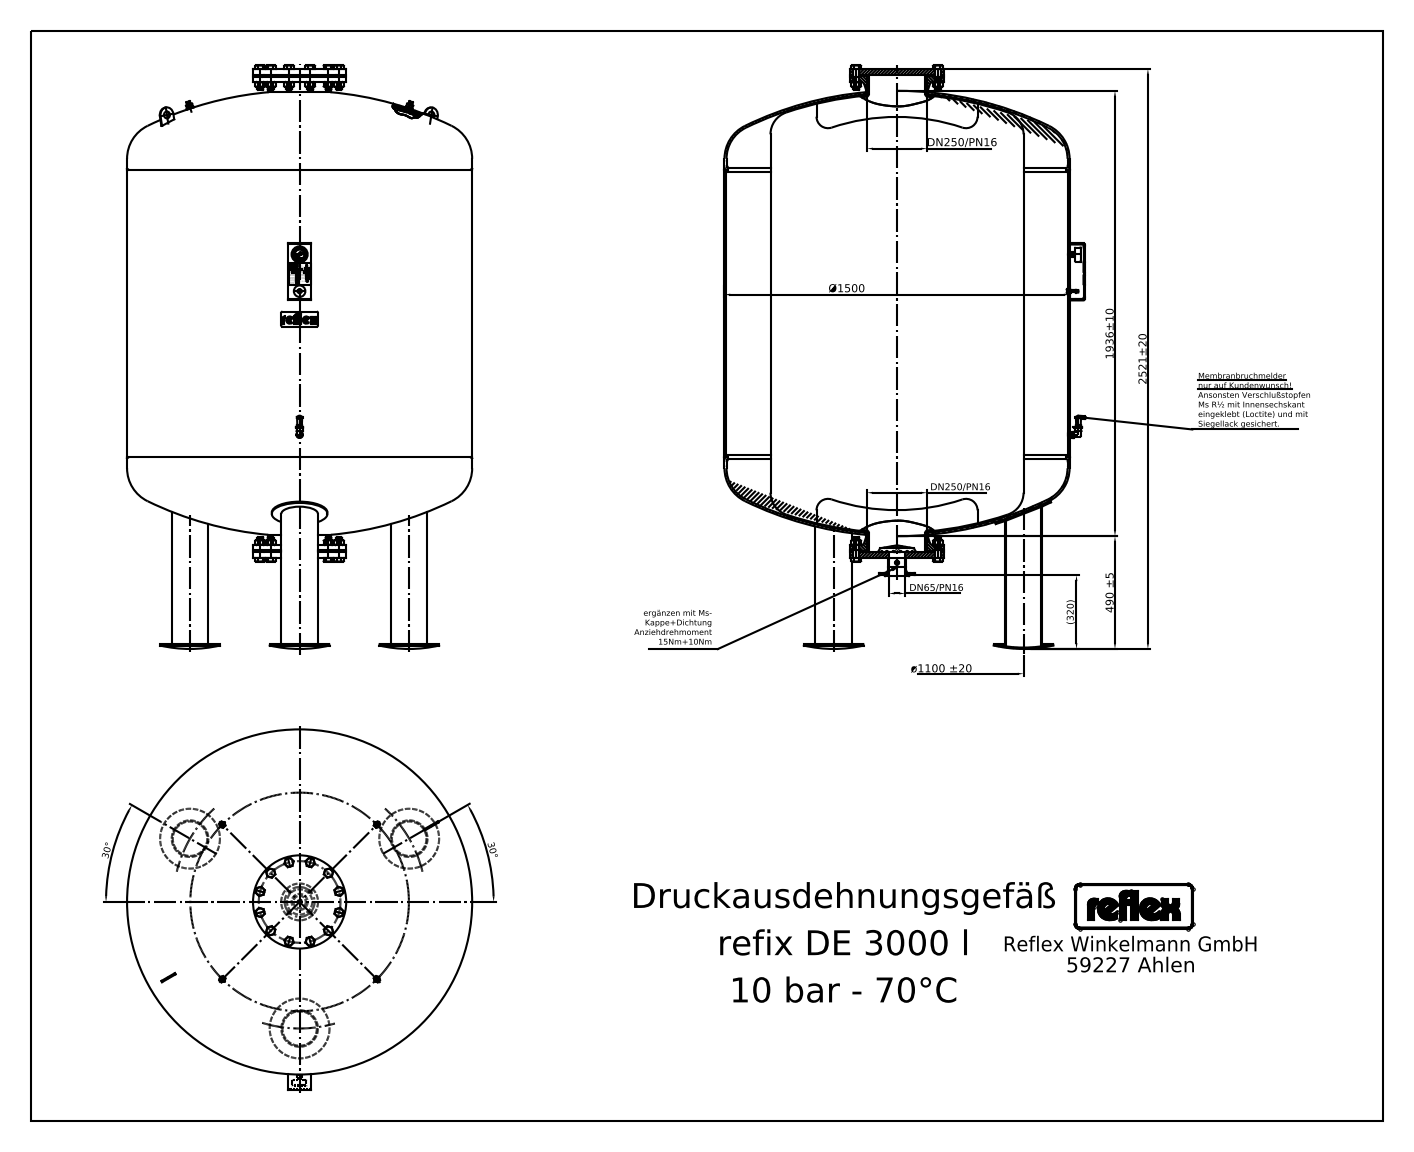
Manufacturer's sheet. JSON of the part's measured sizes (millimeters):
{"step_written_by": "Mechanical Desktop 2008 (CONFIG_CONTROL_DESIGN)", "units": "millimeters", "bodies": {"solids": 20, "faces": 817, "planar": 473, "cylindrical": 190, "other": 154}, "overall_size": [2530, 1566, 1500], "volume_mm3": 3112000000, "surface_area_mm2": 20700000, "round_holes": [[10, 1], [30, 1], [50, 1], [69, 1], [260.4, 1]], "round_bosses_or_shafts": [[16, 12], [159, 3], [28, 2], [26, 2], [20, 2], [1500, 1], [405, 1], [273, 1]], "partial_cylinders_radius": [[5.62, 4], [2.25, 3], [1, 2], [3.84, 2], [5, 2], [6.75, 2], [9.27, 2], [9.4, 2]], "face_to_face_distances": [1276, 26, 2088, 31, 2057, 57, 424, 1700, 2031, 388], "hole_center_spacings": [82.33, 765.5]}
